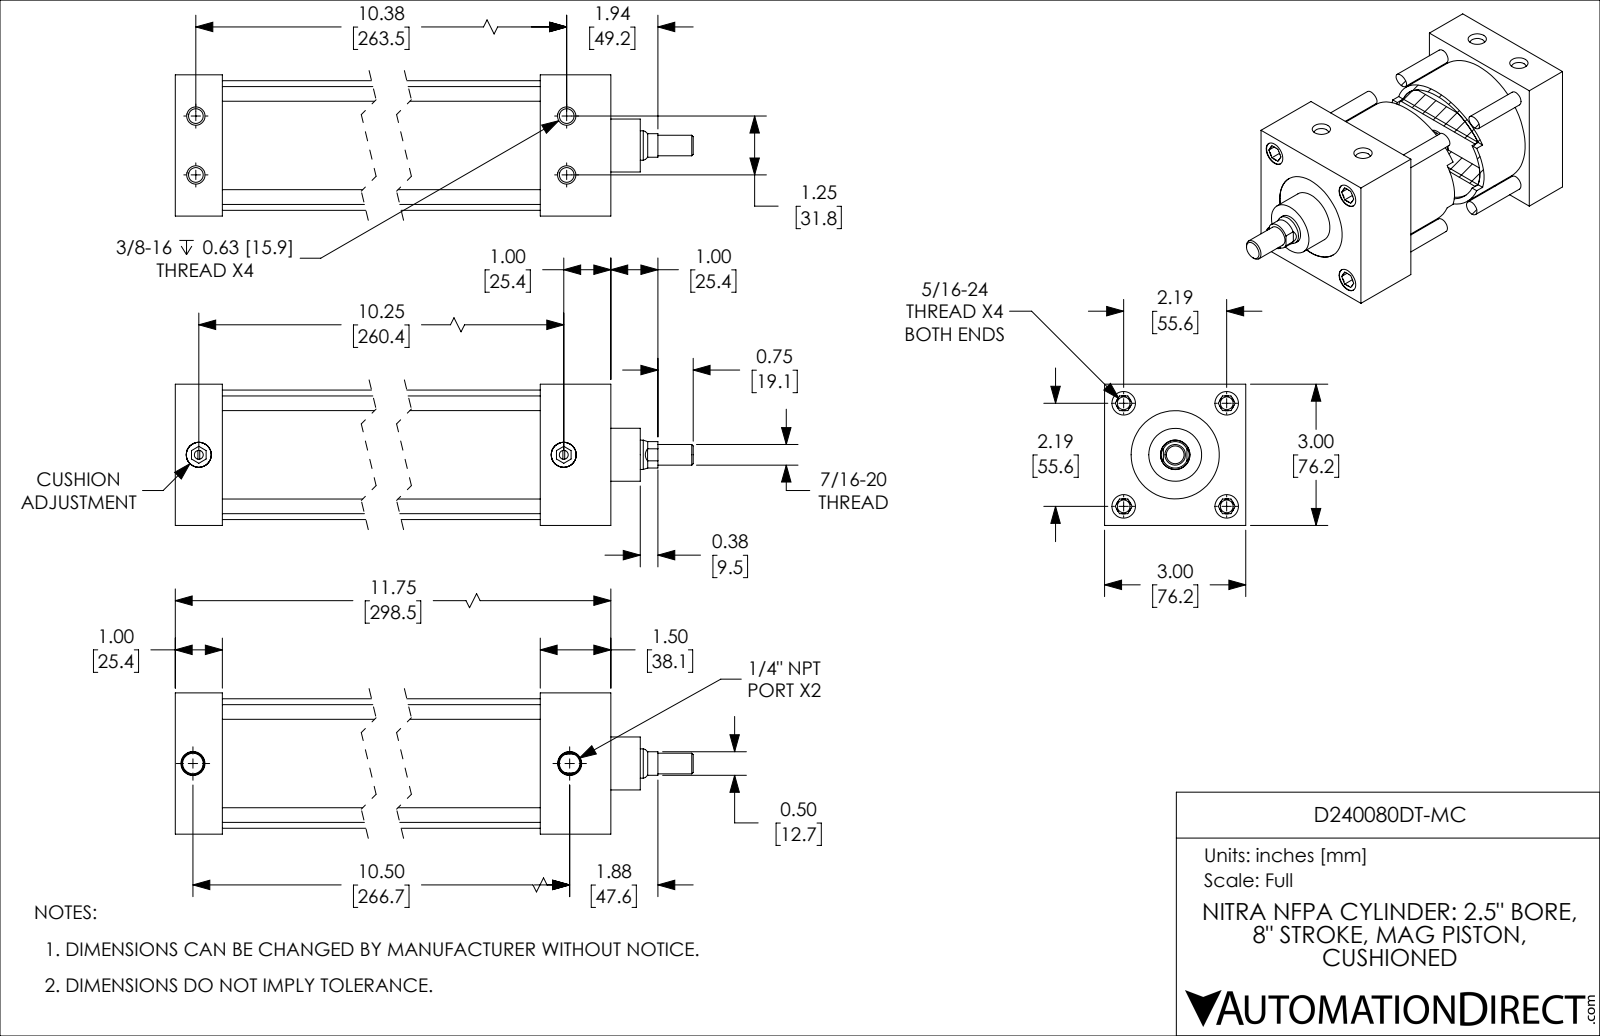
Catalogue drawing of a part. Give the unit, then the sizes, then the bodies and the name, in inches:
Units: inches
Overall size (bounding box): 13.5 × 3 × 3
Round holes (diameter × count): ⌀0.272 ×4, ⌀0.313 ×4, ⌀0.5 ×4, ⌀0.19 ×2, ⌀0.438 ×2, ⌀0.531 ×2, ⌀0.626 ×1, ⌀1.875 ×1, ⌀2.501 ×1
Round bosses / shafts (diameter × count): ⌀0.312 ×4, ⌀0.532 ×2, ⌀2.751 ×1, ⌀2.499 ×1, ⌀1.125 ×1, ⌀0.624 ×1, ⌀0.437 ×1
Partial cylindrical surfaces — rounded edges, fillets, slot ends (radius × count): R0.281 ×1
Main face-to-face distances: 3, 1, 10.25, 9.25, 11.75, 10.75, 1.5, 1.25, 2.25, 8
Hole centre spacings: 1.548, 2.19, 0.628, 0.628, 1.25, 3.097, 10.375, 10.45
Volume: 43.15 in³ · Surface area: 313.3 in²
Bodies: 4 solids, 248 faces (90 planar, 78 cylindrical, 80 other)
Part name (STEP PRODUCT): D240080DT-MC_CUSHION; D240080DT-MC_PISTON_KK1; D240080DT-MC; D240080DT-MC_BODY
STEP written by: SolidWorks 2019 (CONFIG_CONTROL_DESIGN)
